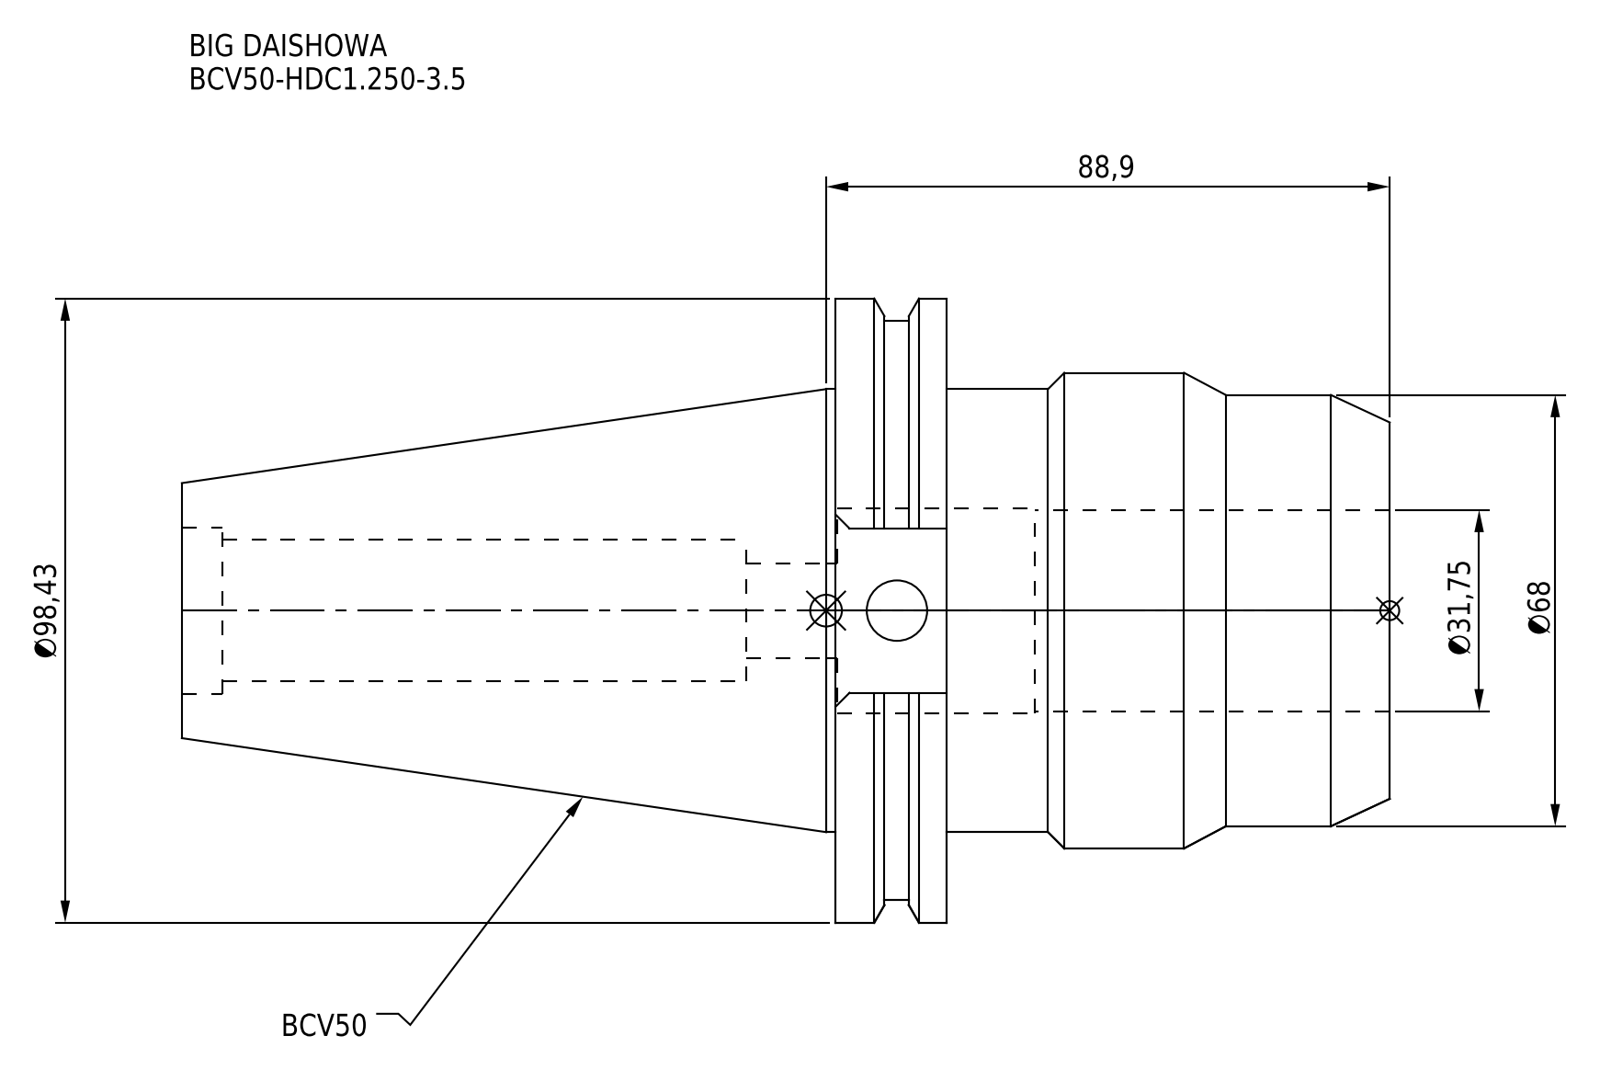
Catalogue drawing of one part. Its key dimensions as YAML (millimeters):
part_name: "BCV50-HDC1_250-3_5"
step_written_by: "CREO PARAMETRIC BY PTC INC, 2016380 (AUTOMOTIVE_DESIGN)"
units: millimeters
bodies: {solids: 1, faces: 51, planar: 16, cylindrical: 25, other: 10}
overall_size: [190.5, 98.42, 96.69]
volume: 540052
surface_area: 67478
round_holes:
  - {diameter: 9.53, count: 1}
  - {diameter: 15, count: 1}
  - {diameter: 22.3, count: 1}
  - {diameter: 26.23, count: 1}
  - {diameter: 31.75, count: 1}
  - {diameter: 32.3, count: 1}
round_bosses_or_shafts:
  - {diameter: 98.42, count: 1}
  - {diameter: 91.29, count: 1}
  - {diameter: 75, count: 1}
  - {diameter: 69.85, count: 1}
  - {diameter: 68, count: 1}
face_to_face_distances: [17.55, 69.85, 87.4, 190.5, 120.65, 103.1, 87.2, 17.35, 103.3, 101.5]
